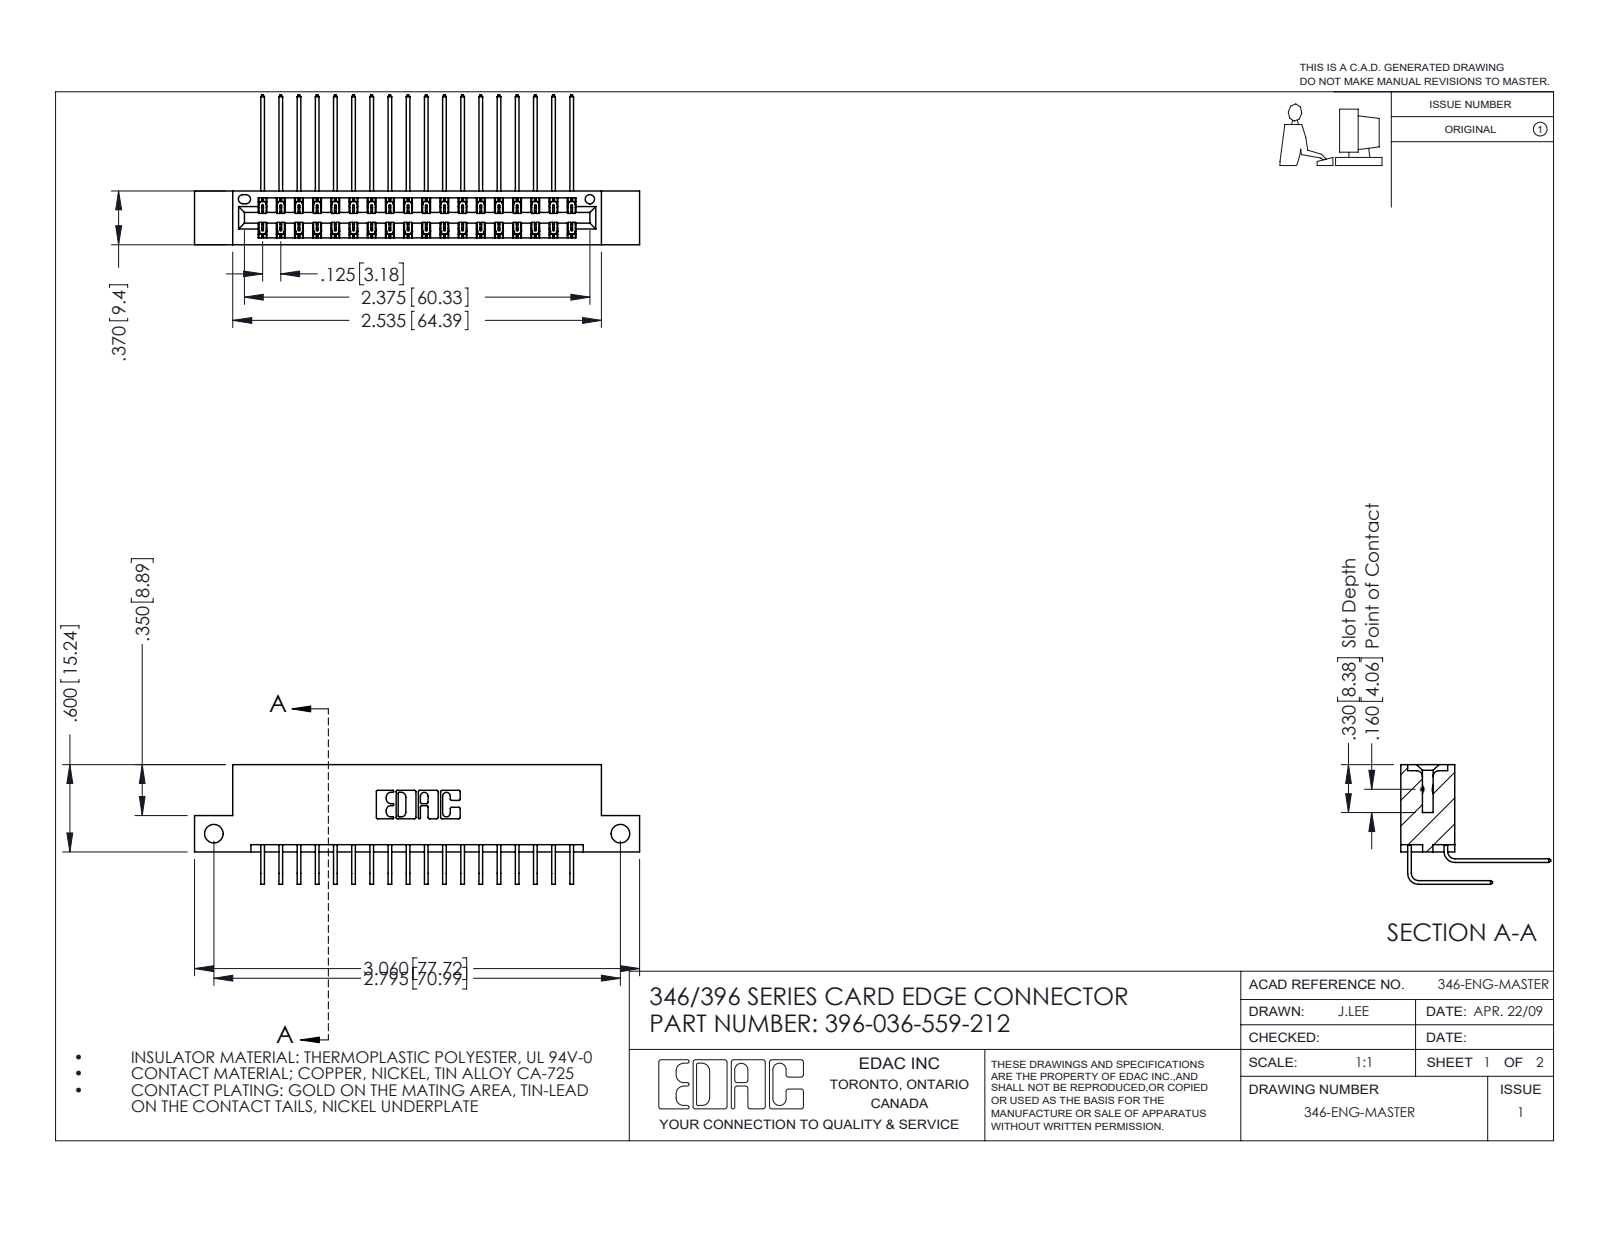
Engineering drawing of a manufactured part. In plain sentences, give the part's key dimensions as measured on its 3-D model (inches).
The part is named "396-036-559-212; 345-292-001_559 Tail - 2; 345-292-001_558 559 Tail - 1; 346 Part_Flush Mounting Lugs - Side Mount". Its 3-D file was written by "SolidWorks 2016 (CONFIG_CONTROL_DESIGN)". It is 37 solids with 2066 faces: 1408 planar, 658 cylindrical and 0 other. Overall it measures 3.06 by 1.03 by 0.823 inches. Its volume is 0.458 cubic inches and its surface area 16.75 square inches. Round holes: 2 of diameter 0.128, 1 of diameter 0.064. Partial cylindrical surfaces (rounded edges, fillets, slot ends): 54 of radius 0.006, 22 of radius 0.01, 6 of radius 0.007, 6 of radius 0.031, 3 of radius 0.026, 2 of radius 0.014, 2 of radius 0.022, 2 of radius 0.024. The main face-to-face distances are 0.048, 0.322, 0.25, 0.025, 0.37, 0.072, 0.298, 0.275, 0.148, 0.222. The hole center spacings are 2.795.
